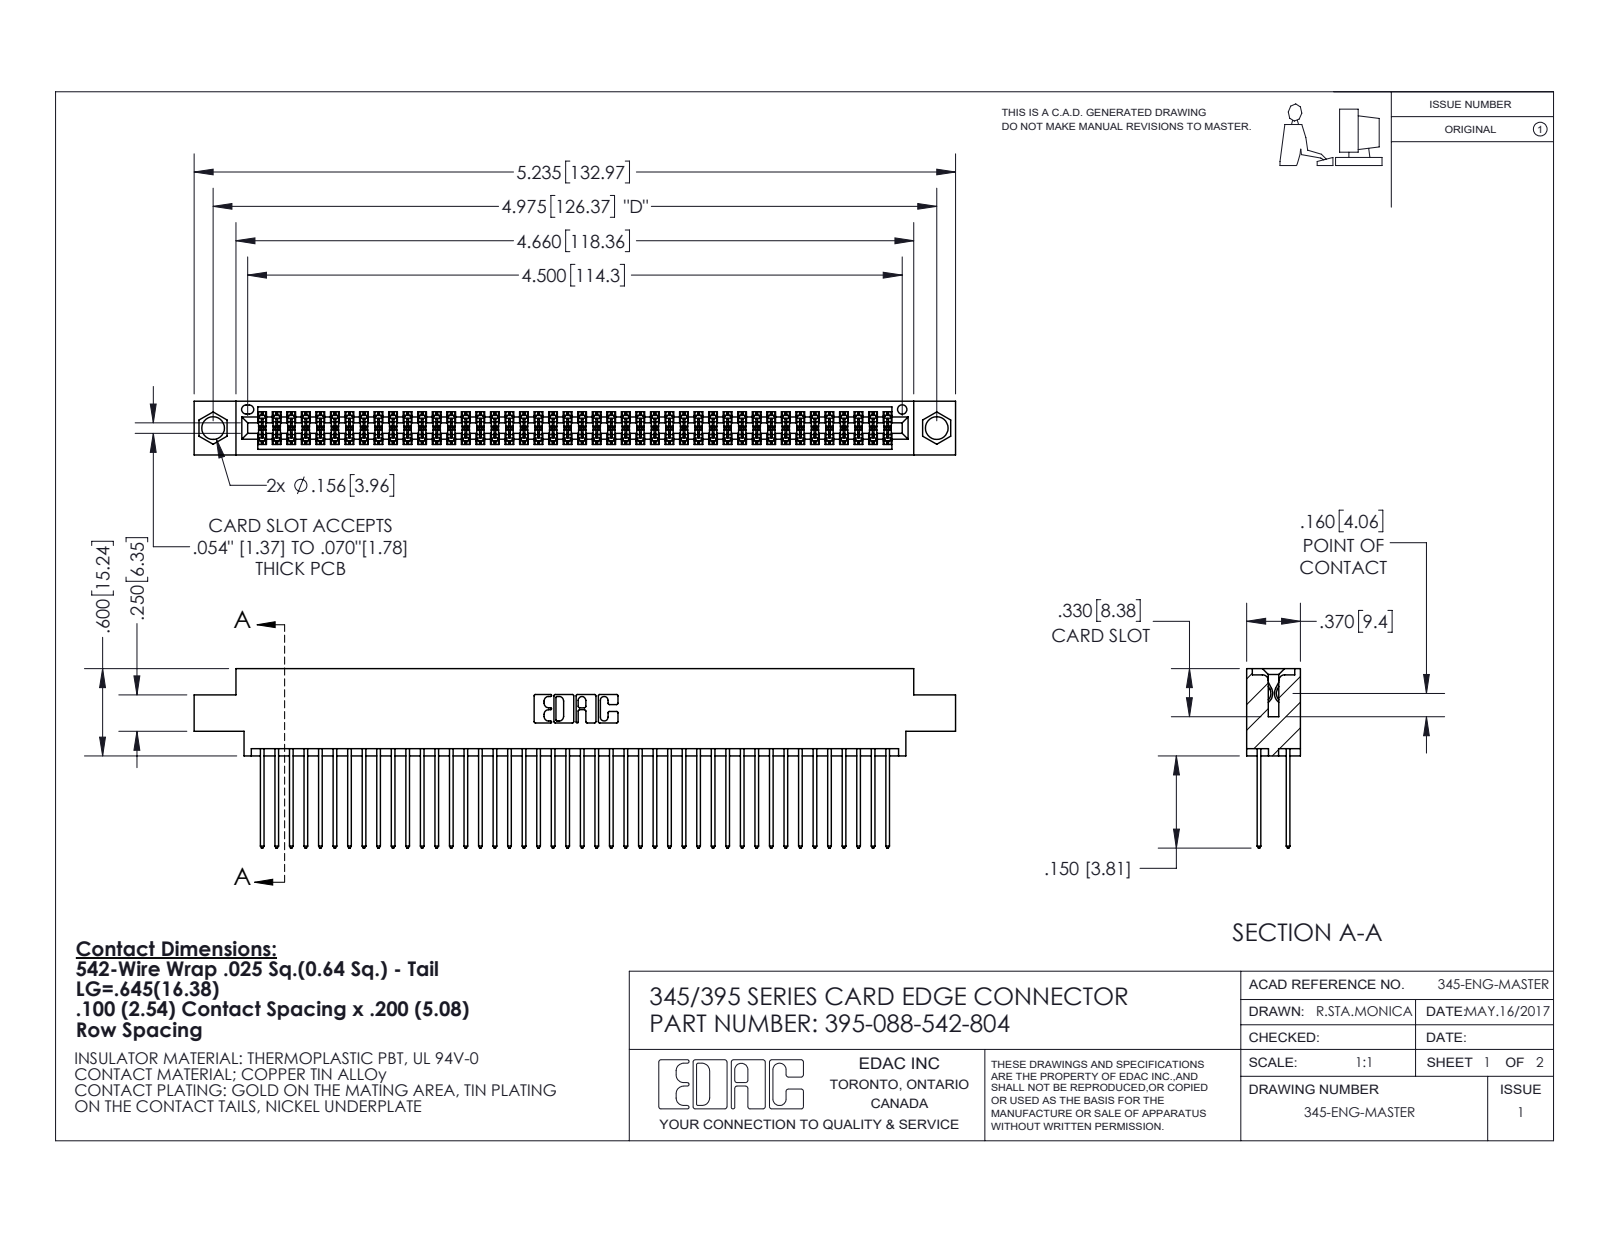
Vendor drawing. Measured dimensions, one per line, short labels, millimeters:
name: 345-292-001_345-293-142; 395-088-542-804; 345 Part_0.170 Offset - 0.156 Dia-TI
written by: SolidWorks 2020 (CONFIG_CONTROL_DESIGN)
unit: mm
bodies: 89 solids, 4544 faces (3002 planar, 1542 cylindrical, 0 other)
size: 133 × 31.3 × 9.4
volume: 13 100 mm³; area: 21 350 mm²
holes: 2× ⌀4, 1× ⌀1.6
rounds: 132× R0.2, 88× R0.3, 22× R0.3, 6× R0.2, 6× R0.8, 3× R0.7, 2× R0.4, 2× R0.5
face distances: 1.8, 7.6, 5.1, 2.5, 6.9, 0.6, 9.4, 5.7, 4.4, 3.8
hole spacings: 6.9, 120.4, 126.4
